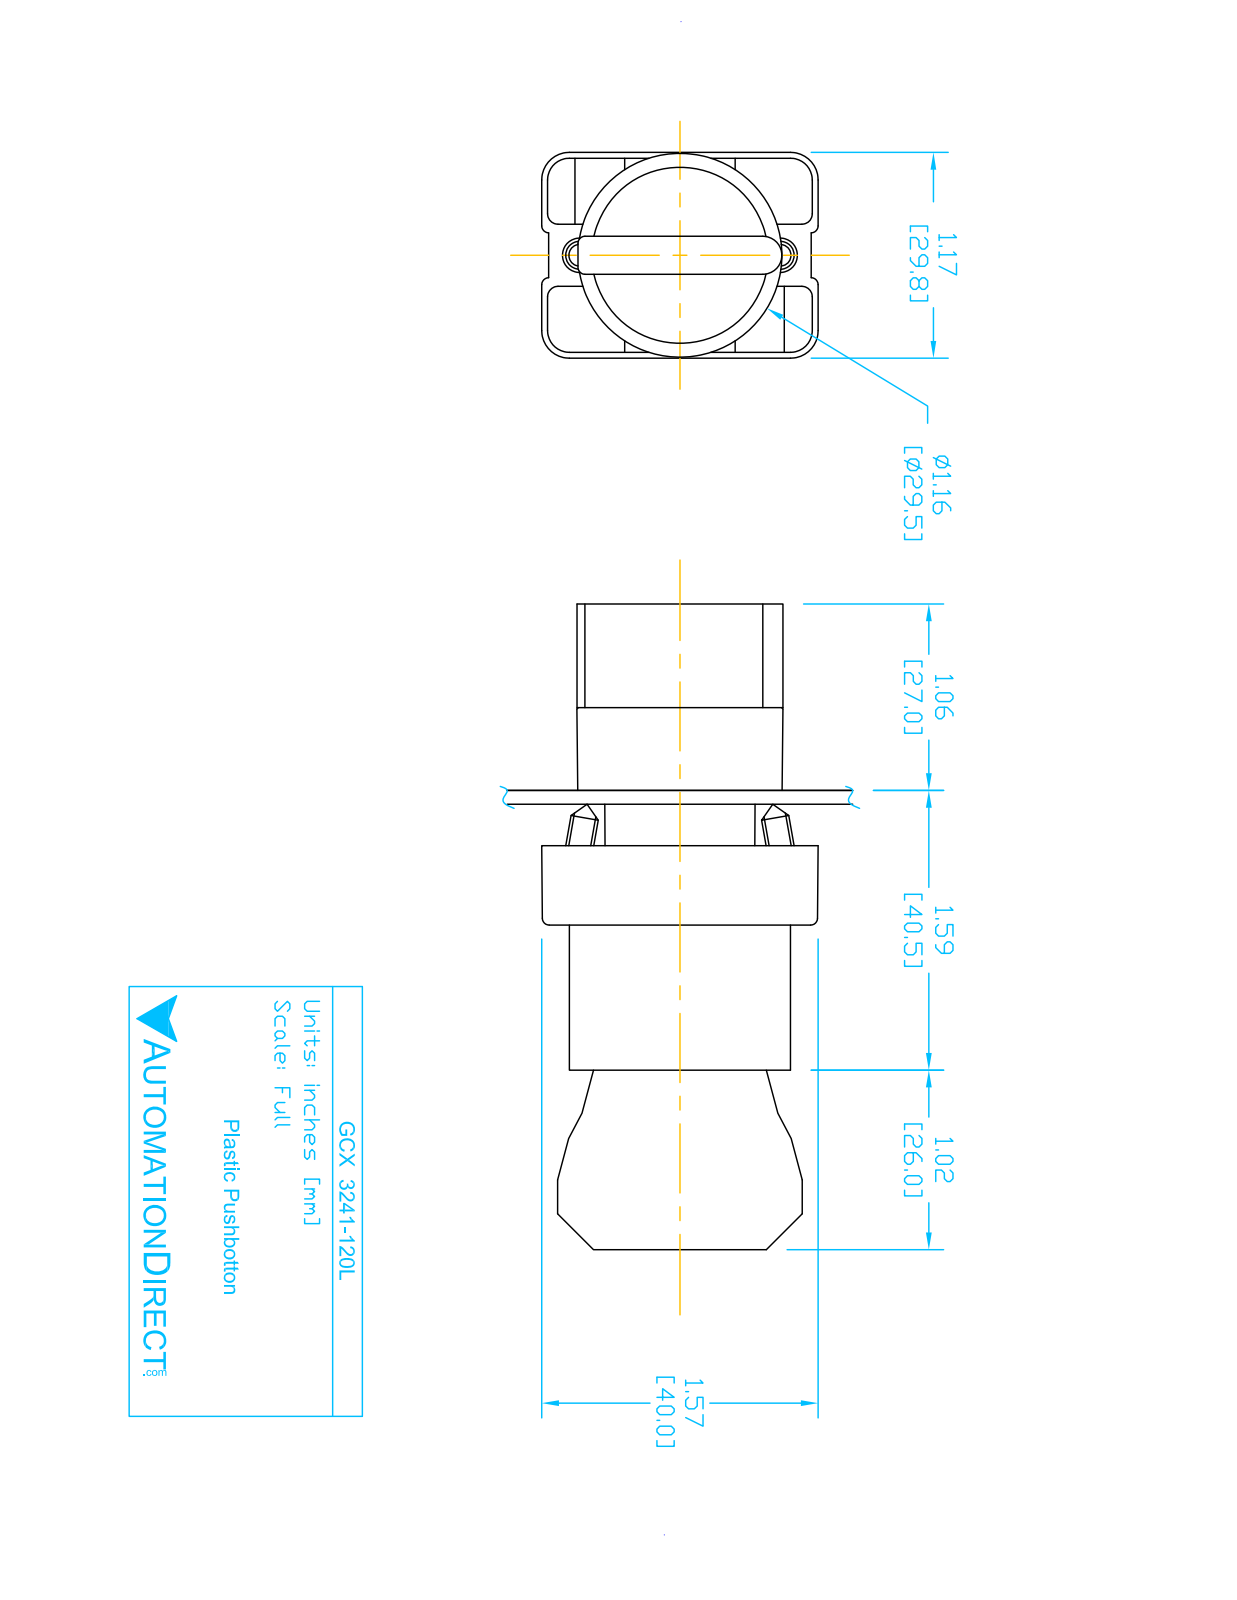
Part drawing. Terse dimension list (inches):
name: GCX3241L OPERATOR; GCX3241-120L; ECX3029-2; ecx1040 (+1 more)
written by: SolidWorks 2016 (AUTOMOTIVE_DESIGN)
unit: in
bodies: 8 solids, 445 faces (263 planar, 151 cylindrical, 31 other)
size: 3.653 × 1.581 × 1.177
volume: 2.799 in³; area: 39 in²
holes: 2× ⌀0.079, 2× ⌀0.124, 2× ⌀0.13, 1× ⌀0.087, 1× ⌀0.197, 1× ⌀0.469, 1× ⌀0.878, 1× ⌀0.888, 1× ⌀1.024
bosses: 4× ⌀0.157, 1× ⌀1.175, 1× ⌀1.004, 1× ⌀0.945, 1× ⌀0.856, 1× ⌀0.78, 1× ⌀0.504
rounds: 24× R0.059, 12× R0.041, 12× R0.124, 12× R0.157, 9× R0.039, 2× R0.128, 1× R0.02, 1× R0.063
face distances: 0.827, 2.02, 1.193, 0.579, 1.244, 1.171, 0.472, 0.469, 0.031, 0.033
hole spacings: 0.236, 0.544, 0.472, 0.49
